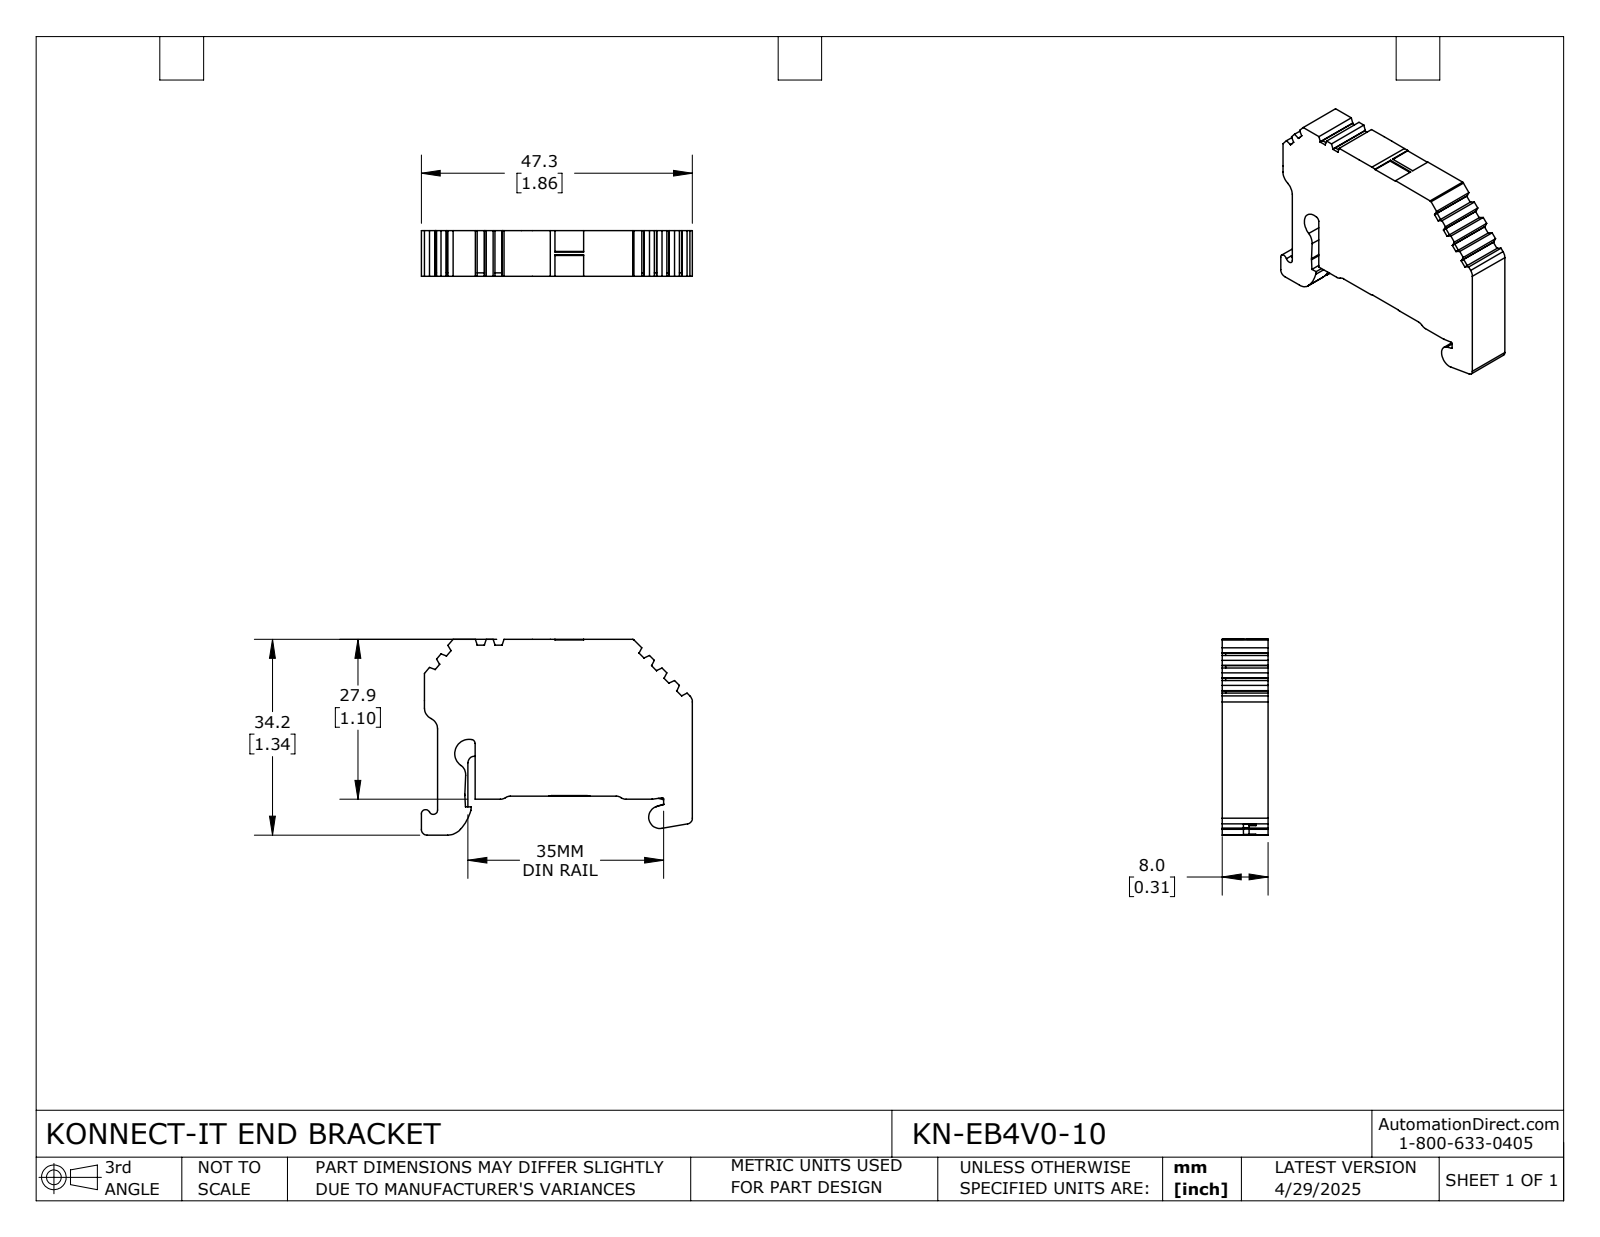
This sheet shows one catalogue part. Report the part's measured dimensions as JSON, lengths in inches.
{"part_name": "KN-EB4V0-10", "step_written_by": "SolidWorks 2024 (CONFIG_CONTROL_DESIGN)", "units": "inches", "bodies": {"solids": 1, "faces": 259, "planar": 168, "cylindrical": 90, "other": 1}, "overall_size": [1.864, 1.345, 0.315], "volume_in3": 0.599, "surface_area_in2": 6.473, "partial_cylinders_radius": [[0.02, 17], [0.059, 5], [0.079, 4], [0.008, 3], [0.012, 3], [0.039, 3], [0.016, 2], [0.03, 2]], "face_to_face_distances": [0.315, 1.752, 1.077, 0.044, 1.073, 0.115, 0.258, 1.494, 0.021, 1.098]}
